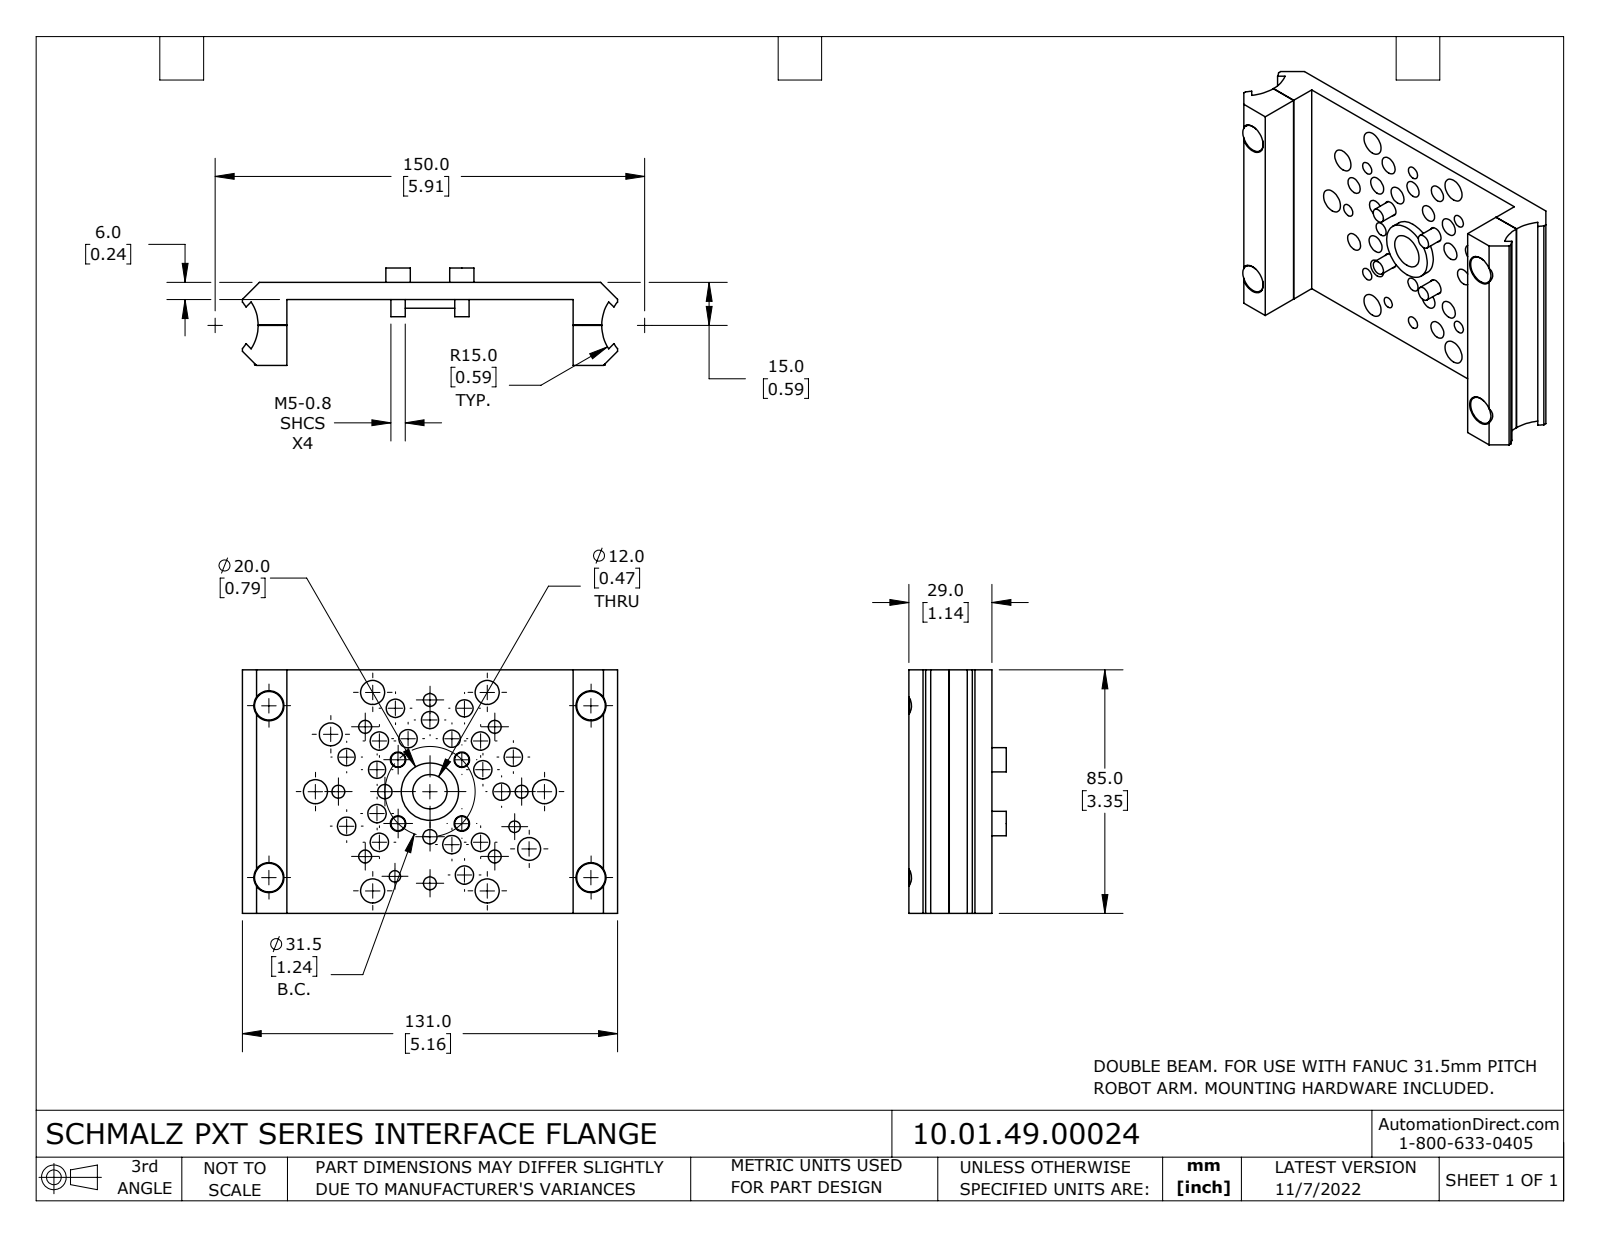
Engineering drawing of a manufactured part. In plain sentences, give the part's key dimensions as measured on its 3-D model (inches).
The part is named "10.01.49.00024". Its 3-D file was written by "SolidWorks 2021 (CONFIG_CONTROL_DESIGN)". It is 12 solids with 217 faces: 61 planar, 156 cylindrical and 0 other. Overall it measures 5.157 by 3.346 by 1.339 inches. Its volume is 6.361 cubic inches and its surface area 73.99 square inches. Round holes: 12 of diameter 0.252, 8 of diameter 0.177, 6 of diameter 0.197, 6 of diameter 0.236, 6 of diameter 0.331, 4 of diameter 0.213, 4 of diameter 0.248, 4 of diameter 0.413, 2 of diameter 0.157, 2 of diameter 0.315, 1 of diameter 0.472, 1 of diameter 0.63. Round bosses or shafts: 4 of diameter 0.394, 4 of diameter 0.335, 4 of diameter 0.236, 4 of diameter 0.197, 1 of diameter 0.787. Partial cylindrical surfaces (rounded edges, fillets, slot ends): 2 of radius 0.492, 2 of radius 0.591. The main face-to-face distances are 0.236, 3.937, 0.354, 0.551, 0.587, 0.35, 0.591, 1.142, 0.906, 0.555. The hole center spacings are 1.575, 1.722, 2.01, 1.26, 0.964, 2.328, 0.484, 0.611.
